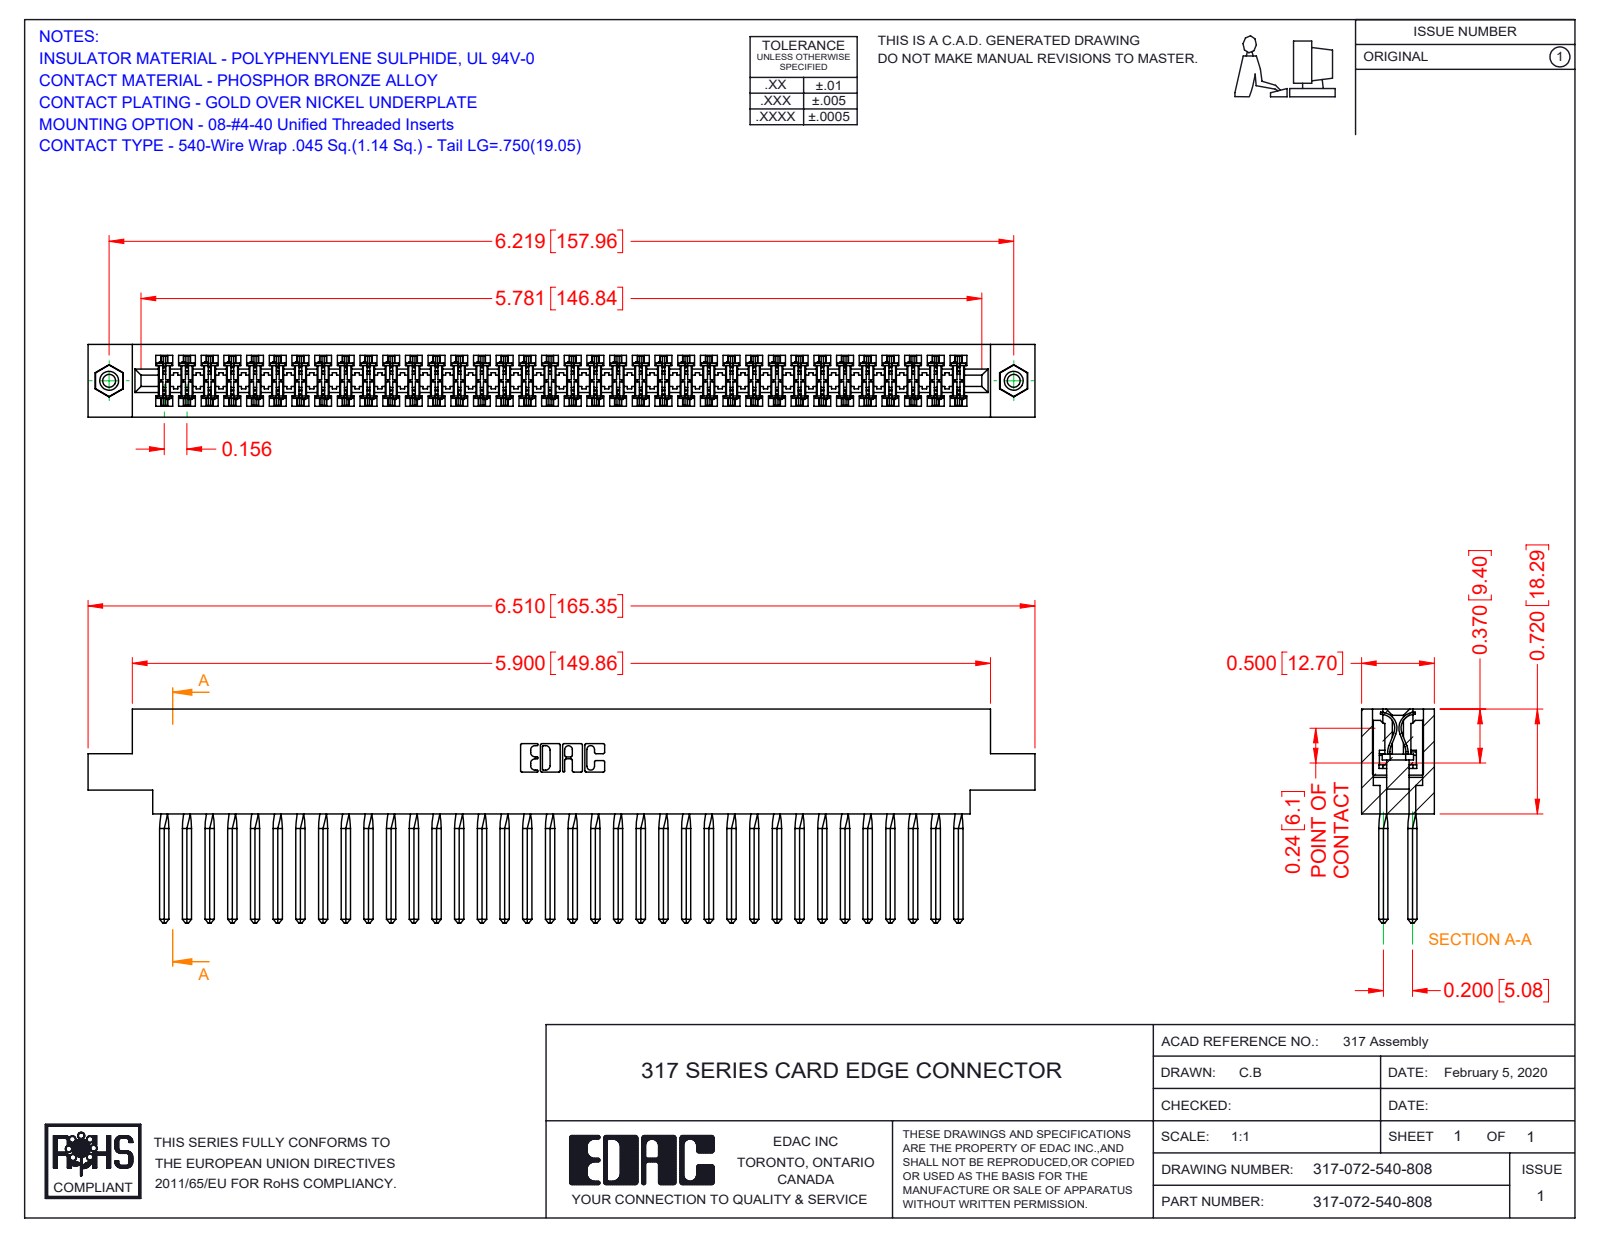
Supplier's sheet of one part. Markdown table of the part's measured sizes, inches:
| quantity | value |
| --- | --- |
| part name | 317 Part_.156 Dia - TI; 317-072-540-878; 345-250-001_345-250-003-102; 317-290-001_540 |
| STEP written by | SolidWorks 2016 (CONFIG_CONTROL_DESIGN) |
| units | inches |
| bodies | 75 solids, 6570 faces (5346 planar, 920 cylindrical, 304 other) |
| overall size | 6.51 × 1.47 × 0.5 |
| volume | 1.681 in³ |
| surface area | 63.33 in² |
| round holes (diameter × count) | 0.089 × 2, 0.125 × 2, 0.156 × 2 |
| round bosses / shafts (diameter × count) | 0.155 × 2 |
| partial cylindrical surfaces (radius × count) | 0.015 × 144, 0.01 × 22, 0.007 × 6, 0.031 × 6, 0.026 × 3, 0.095 × 2, 0.1 × 2, 0.11 × 2 |
| main face-to-face distances | 0.5, 0.075, 0.425, 0.35, 0.195, 0.11, 0.094, 0.2, 0.115, 0.131 |
| hole center spacings | 6.219 |
